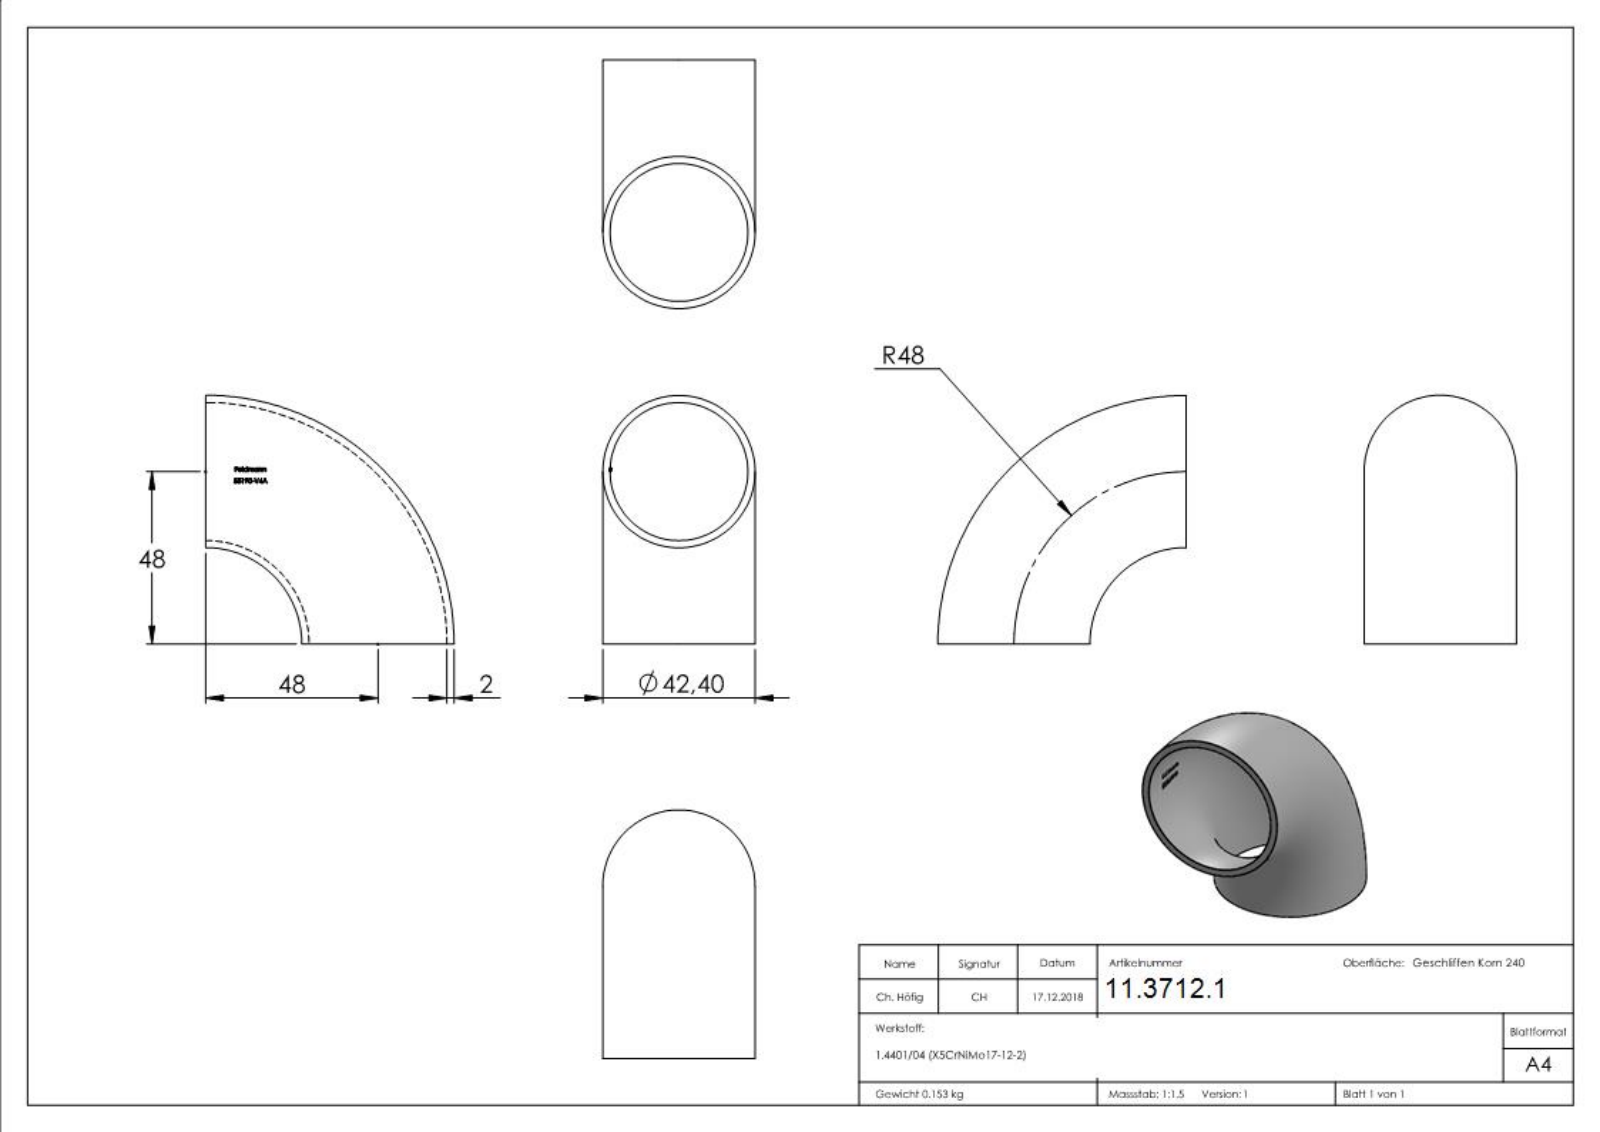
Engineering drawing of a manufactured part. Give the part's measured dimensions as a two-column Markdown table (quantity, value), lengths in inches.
| quantity | value |
| --- | --- |
| part name | 55190-V4A |
| STEP written by | SolidWorks 2015 (CONFIG_CONTROL_DESIGN) |
| units | inches |
| bodies | 1 solid, 222 faces (112 planar, 0 cylindrical, 110 other) |
| overall size | 2.724 × 2.724 × 1.669 |
| volume | 1.168 in³ |
| surface area | 30.47 in² |
| main face-to-face distances | 0.156, 0.015, 0.117, 0.161, 0.035, 0.132, 0.047, 0.02, 0.024, 0.08 |
